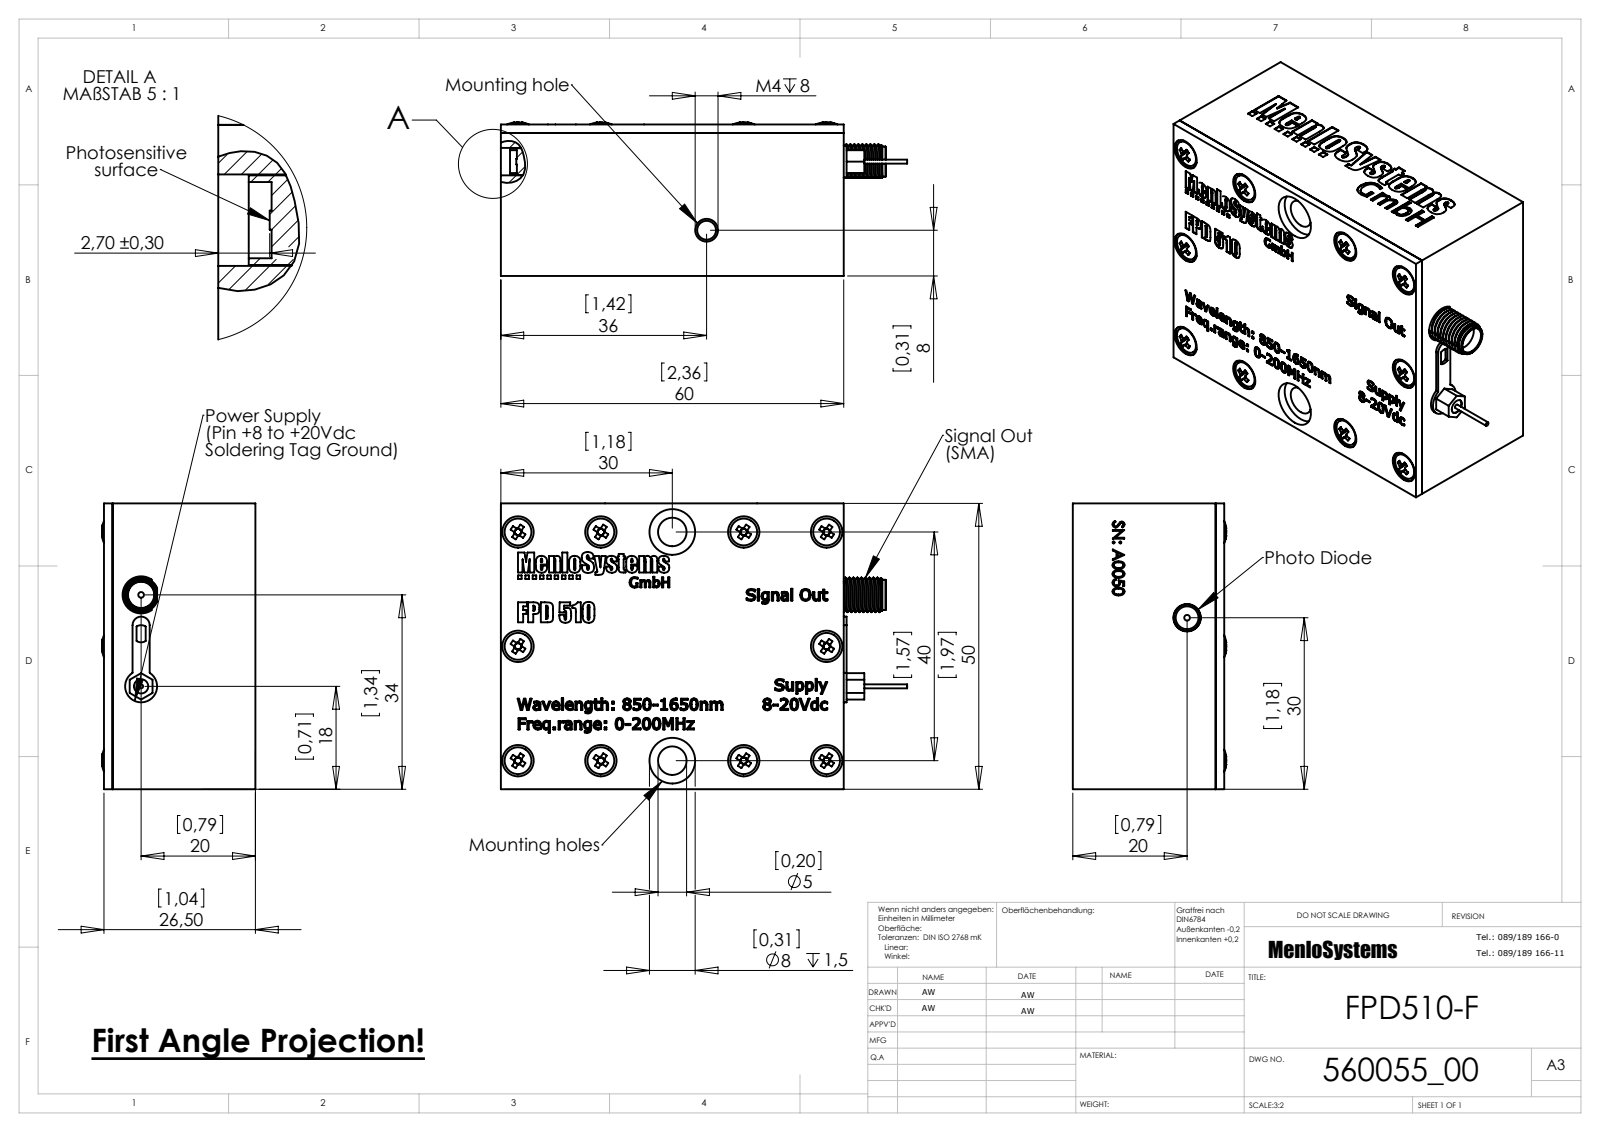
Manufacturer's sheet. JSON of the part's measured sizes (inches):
{"part_name": "313600_Standard; PIN-Diode_G8376; 316322_Pos2; 600238_FPD510F (+4 more)", "step_written_by": "SolidWorks 2007 (AUTOMOTIVE_DESIGN)", "units": "inches", "bodies": {"solids": 17, "faces": 2469, "planar": 1313, "cylindrical": 172, "other": 984}, "overall_size": [2.799, 1.969, 1.057], "volume_in3": 4.763, "surface_area_in2": 34.81, "round_holes": [[0.098, 11], [0.081, 10], [0.217, 10], [0.157, 2], [0.197, 2], [0.315, 2], [0.039, 1], [0.118, 1], [0.13, 1], [0.181, 1], [0.189, 1]], "round_bosses_or_shafts": [[0.185, 11], [0.02, 6], [0.24, 1], [0.22, 1], [0.213, 1], [0.208, 1], [0.039, 1], [0.028, 1]], "partial_cylinders_radius": [[0.039, 4], [0.079, 4], [0.059, 2], [0.08, 2], [0.128, 1]], "face_to_face_distances": [0.984, 0.059, 1.043, 0.079, 0.02, 0.965, 1.969, 2.362, 1.965, 0.394], "hole_center_spacings": [1.575, 0.492, 0.571, 0.787, 0.972, 1.063, 1.323, 1.555]}
